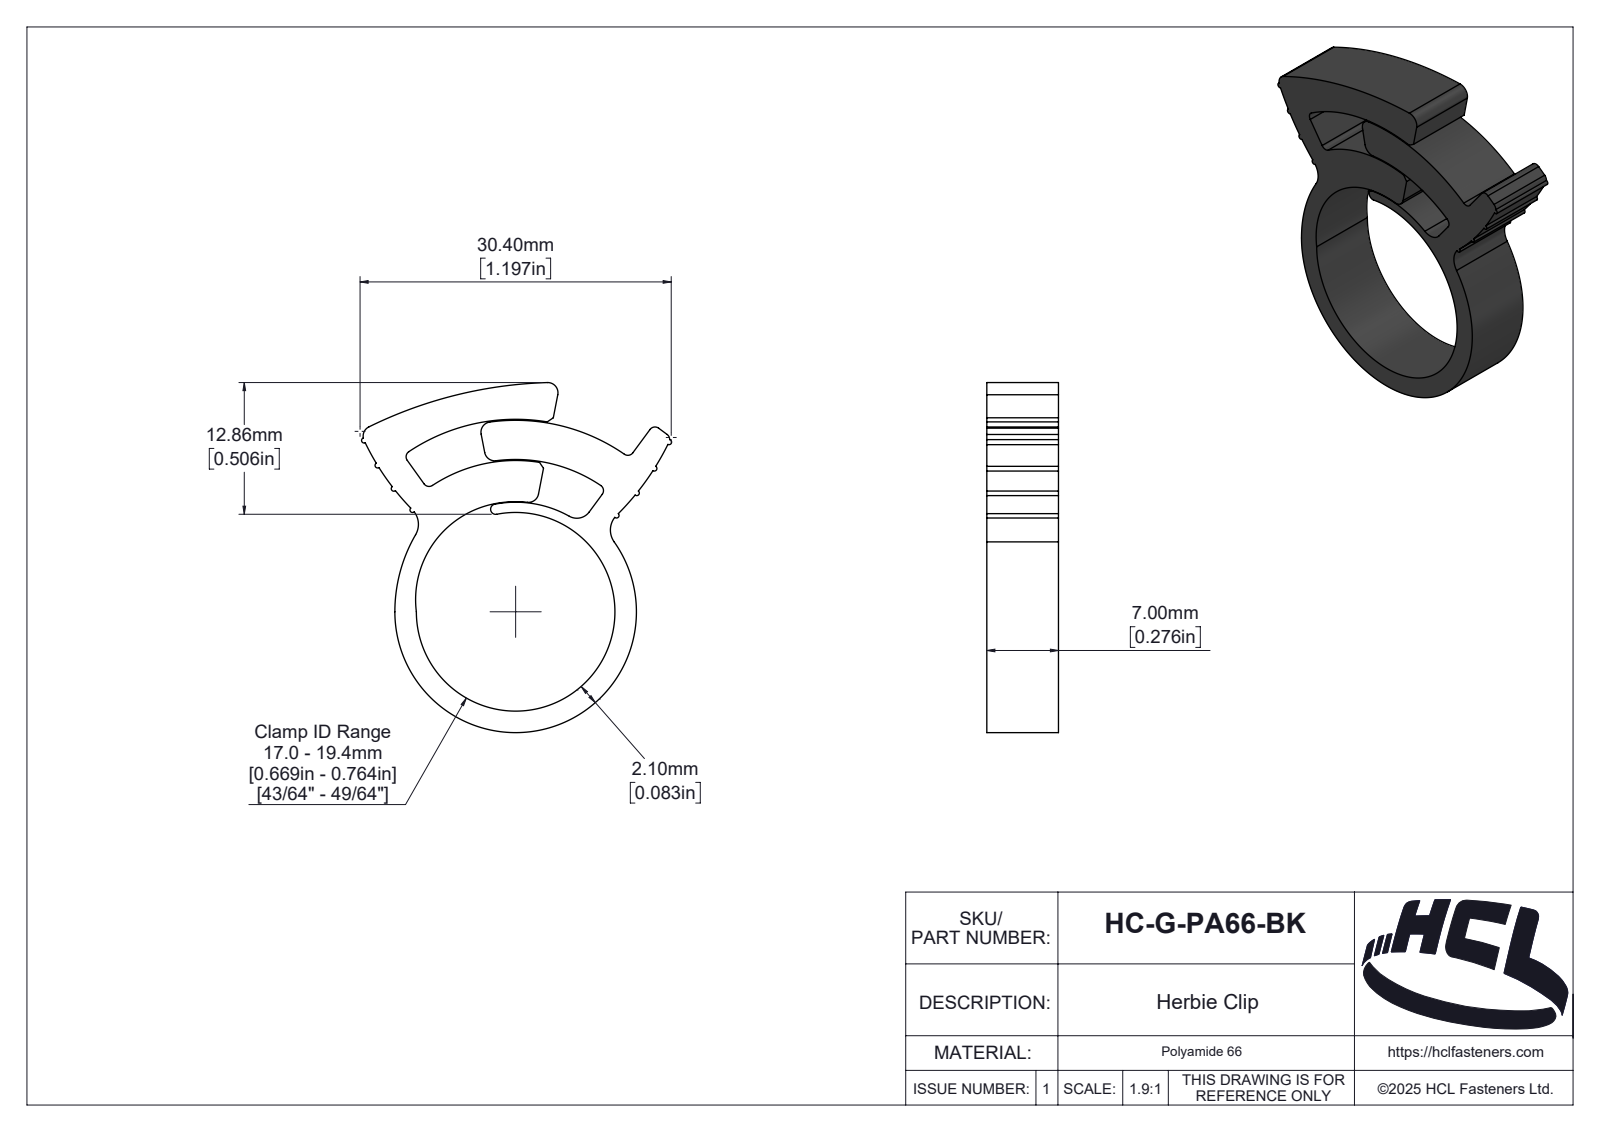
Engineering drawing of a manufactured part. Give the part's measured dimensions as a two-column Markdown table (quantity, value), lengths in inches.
| quantity | value |
| --- | --- |
| part name | HC-G-PA66-BK |
| STEP written by | SolidWorks 2025 (AUTOMOTIVE_DESIGN) |
| units | inches |
| bodies | 1 solid, 162 faces (13 planar, 100 cylindrical, 49 other) |
| overall size | 1.346 × 1.193 × 0.276 |
| volume | 0.14 in³ |
| surface area | 3.756 in² |
| partial cylindrical surfaces (radius × count) | 0.01 × 8, 0.024 × 6, 0.039 × 5, 0.079 × 2, 0.007 × 1, 0.02 × 1, 0.026 × 1, 0.033 × 1 |
| main face-to-face distances | 0.276 |
